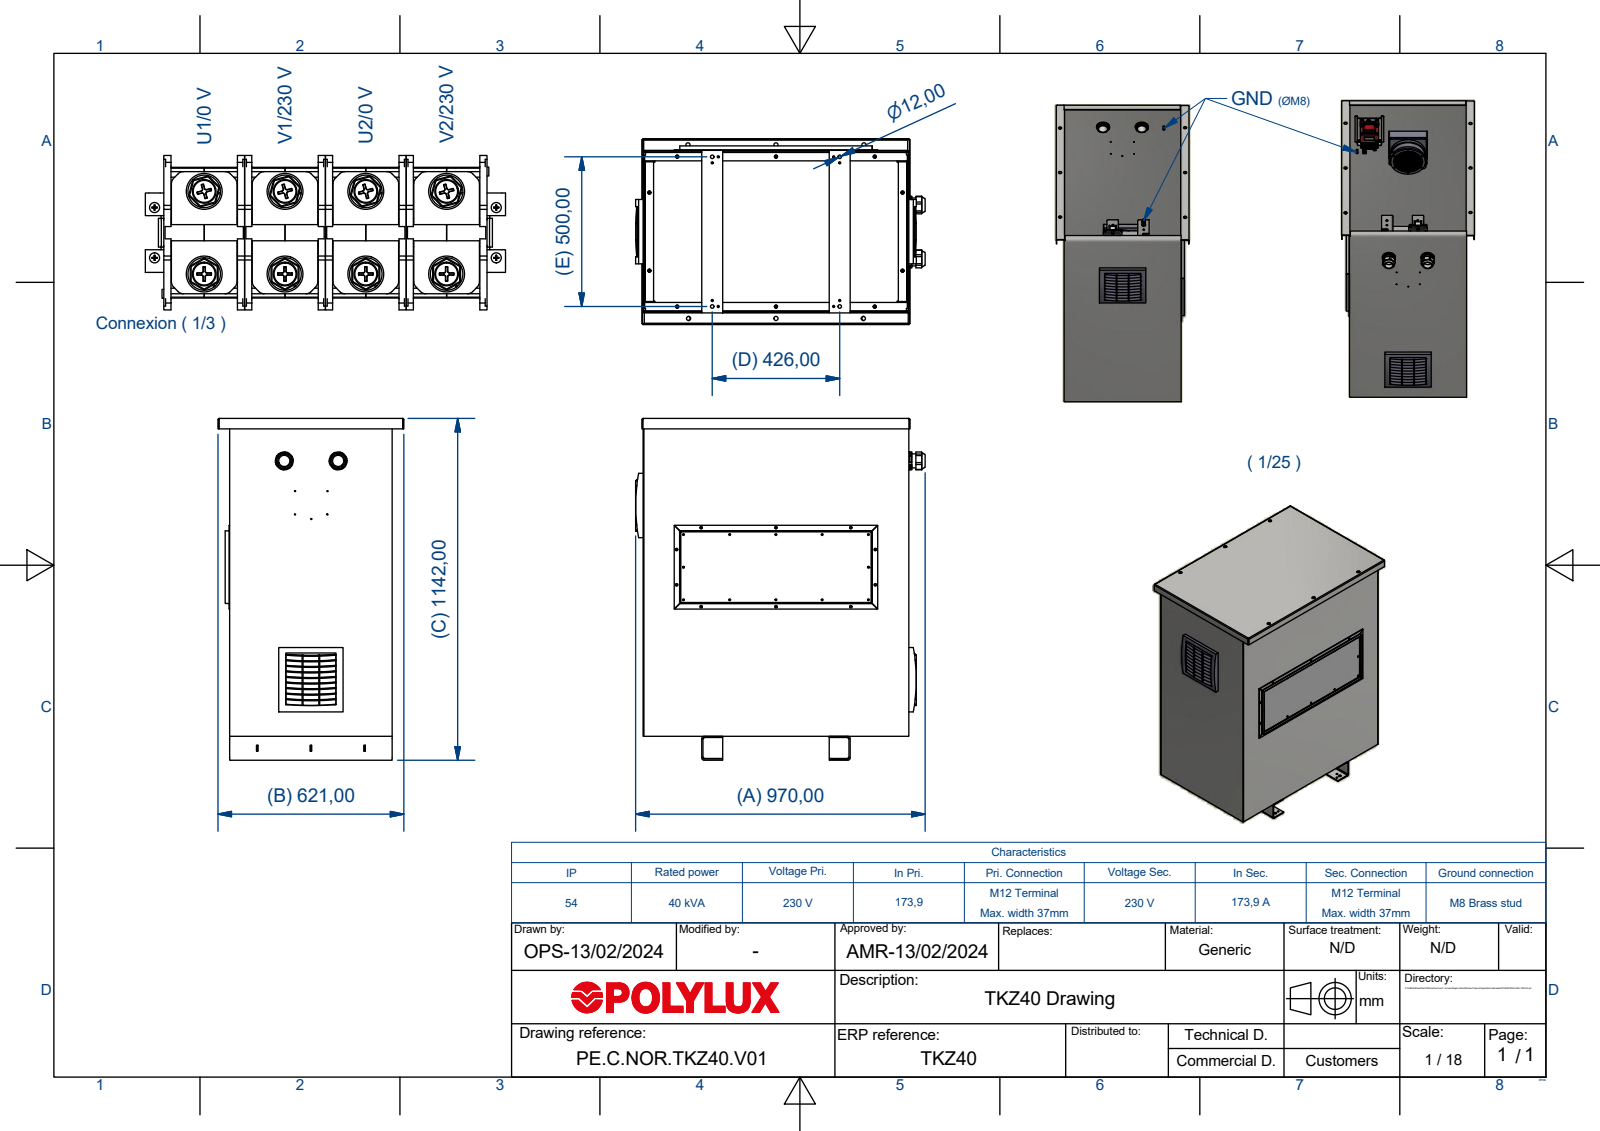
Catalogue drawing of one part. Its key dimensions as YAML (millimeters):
part_name: "CAJ90-100C54"
step_written_by: "Autodesk Inventor 2018 (AUTOMOTIVE_DESIGN)"
units: millimeters
bodies: {solids: 43, faces: 4591, planar: 2946, cylindrical: 1268, other: 377}
overall_size: [1142, 967.5, 621]
volume: 83490000
surface_area: 13260000
round_holes:
  - {diameter: 7, count: 30}
  - {diameter: 6, count: 18}
  - {diameter: 12, count: 13}
  - {diameter: 14, count: 12}
  - {diameter: 3.81, count: 10}
  - {diameter: 6.65, count: 10}
  - {diameter: 8, count: 10}
  - {diameter: 10, count: 10}
  - {diameter: 10.2, count: 10}
  - {diameter: 3.5, count: 5}
  - {diameter: 11, count: 4}
  - {diameter: 13, count: 4}
round_bosses_or_shafts:
  - {diameter: 0.7, count: 5}
  - {diameter: 8, count: 3}
  - {diameter: 1.27, count: 3}
  - {diameter: 130.16, count: 2}
  - {diameter: 107.72, count: 2}
  - {diameter: 85.28, count: 2}
  - {diameter: 60, count: 2}
  - {diameter: 47, count: 2}
partial_cylinders:
  - {radius: 3, count: 63}
  - {radius: 2, count: 56}
  - {radius: 1, count: 49}
  - {radius: 4, count: 42}
  - {radius: 1.25, count: 40}
  - {radius: 701.39, count: 38}
  - {radius: 3.5, count: 15}
  - {radius: 0.5, count: 12}
face_to_face_distances: [2, 541, 543, 886, 539, 1060, 4, 888, 884, 1062]
hole_center_spacings: [63.32, 154.5, 267.2, 309, 378.16, 513.99, 218, 580]
